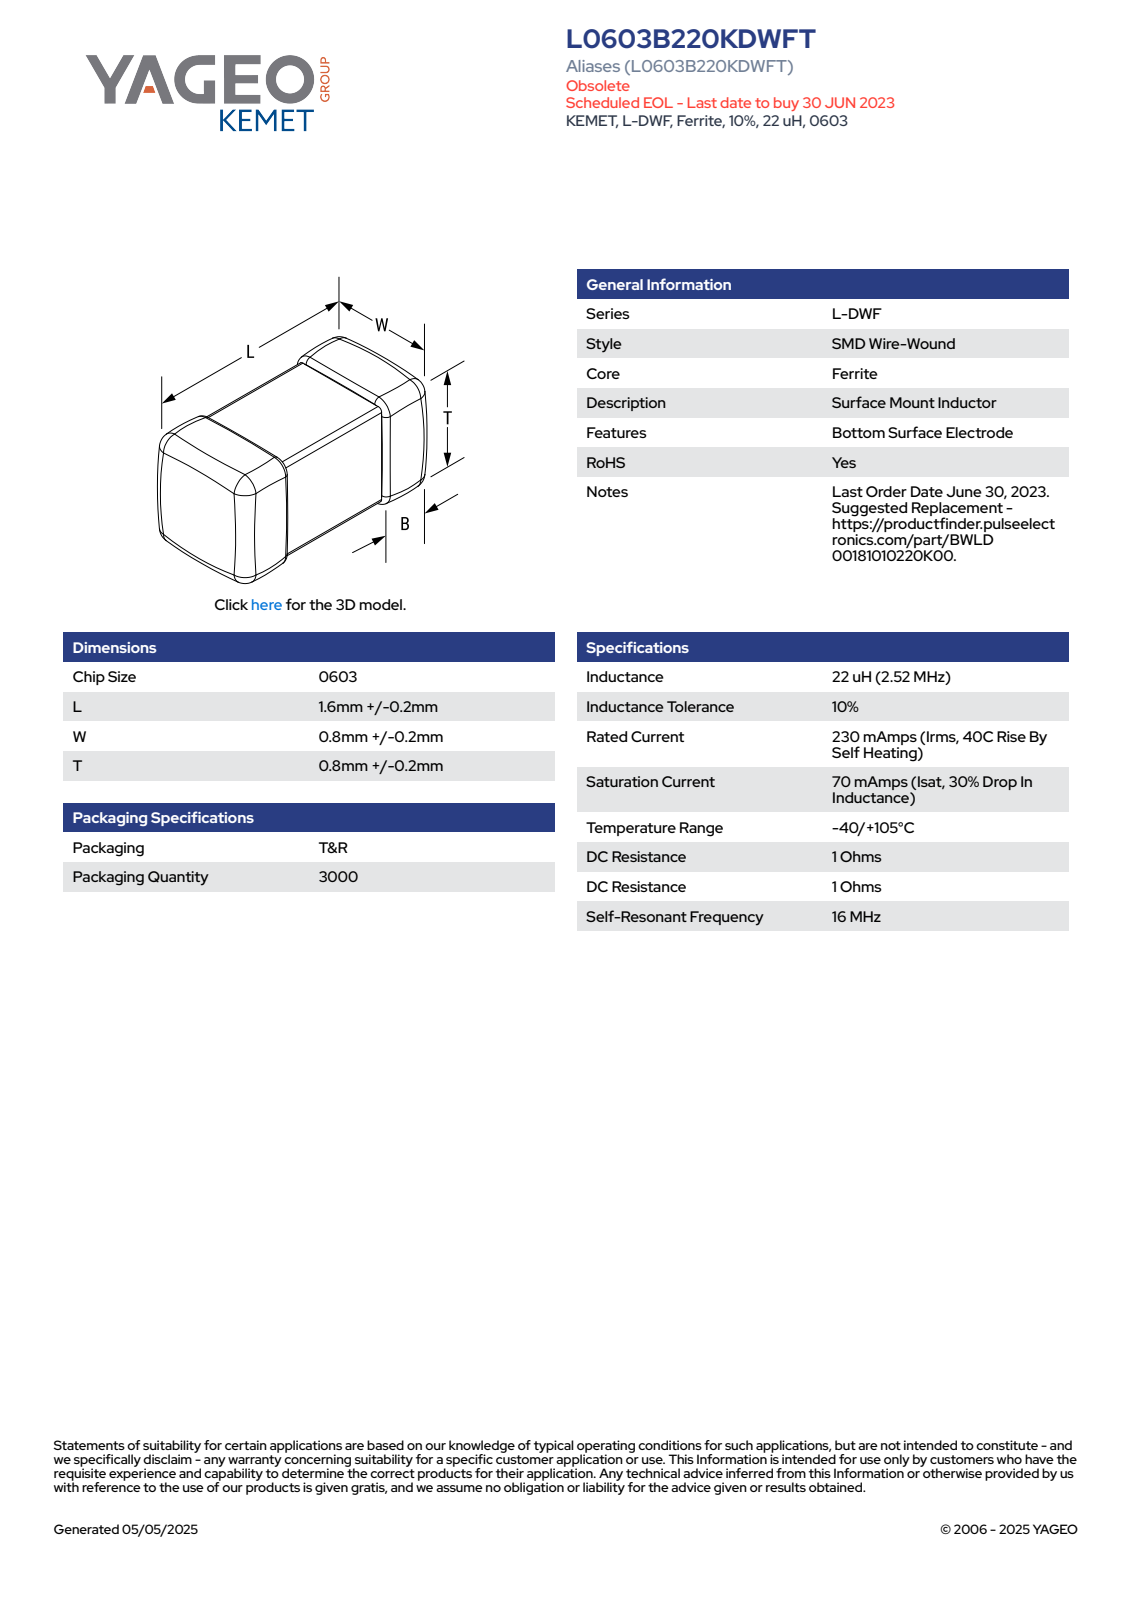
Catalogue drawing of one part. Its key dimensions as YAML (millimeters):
part_name: "IS_KC_0603_L1.8W1T1LL0.55"
step_written_by: "SolidWorks 2014 (AUTOMOTIVE_DESIGN)"
units: millimeters
bodies: {solids: 4, faces: 73, planar: 73, cylindrical: 0, other: 0}
overall_size: [1.8, 1, 1]
volume: 2
surface_area: 9
face_to_face_distances: [0.98, 1, 0.96, 1.8, 0.55, 1.25, 0.7, 0.99, 0.97, 0.41]
